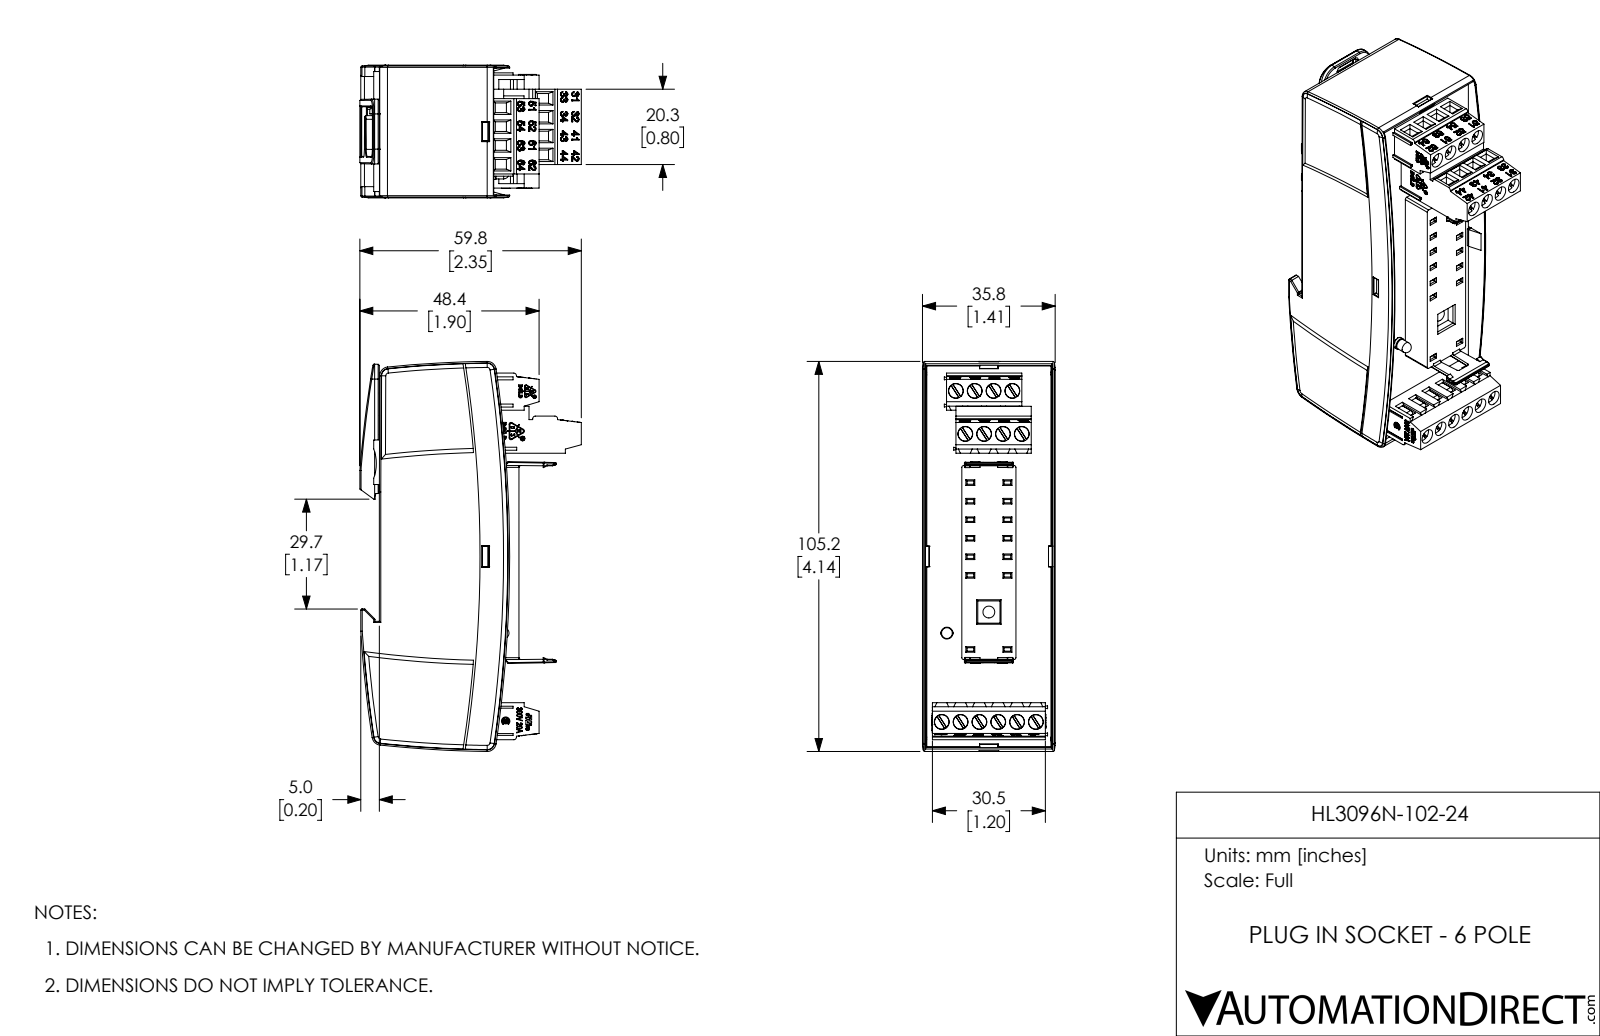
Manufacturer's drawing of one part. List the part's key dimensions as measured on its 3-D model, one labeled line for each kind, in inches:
Part name (STEP PRODUCT): HL3096N-102-24
STEP written by: SolidWorks 2017 (AUTOMOTIVE_DESIGN)
Units: inches
Bodies: 3 solids, 3929 faces (2637 planar, 627 cylindrical, 665 other)
Overall size (bounding box): 4.142 × 2.352 × 1.409
Volume: 7.963 in³ · Surface area: 50.1 in²
Round holes (diameter × count): ⌀0.059 ×27, ⌀0.157 ×14, ⌀0.022 ×2, ⌀0.035 ×2, ⌀0.019 ×1, ⌀0.034 ×1, ⌀0.037 ×1, ⌀0.05 ×1, ⌀0.06 ×1, ⌀0.126 ×1
Round bosses / shafts (diameter × count): ⌀0.154 ×14, ⌀0.019 ×2, ⌀0.126 ×1, ⌀0.114 ×1, ⌀0.046 ×1, ⌀0.037 ×1, ⌀0.034 ×1, ⌀0.022 ×1
Partial cylindrical surfaces — rounded edges, fillets, slot ends (radius × count): R0.008 ×53, R0.012 ×14, R0.02 ×13, R0.006 ×12, R0.004 ×7, R0.005 ×6, R0.005 ×6, R0.006 ×6
Main face-to-face distances: 1.402, 1.409, 1.394, 1.154, 0.992, 0.417, 0.409, 0.984, 1.484, 0.331
Hole centre spacings: 0.2, 0.4, 0.394, 0.197, 0.467, 0.608, 0.246, 0.6
